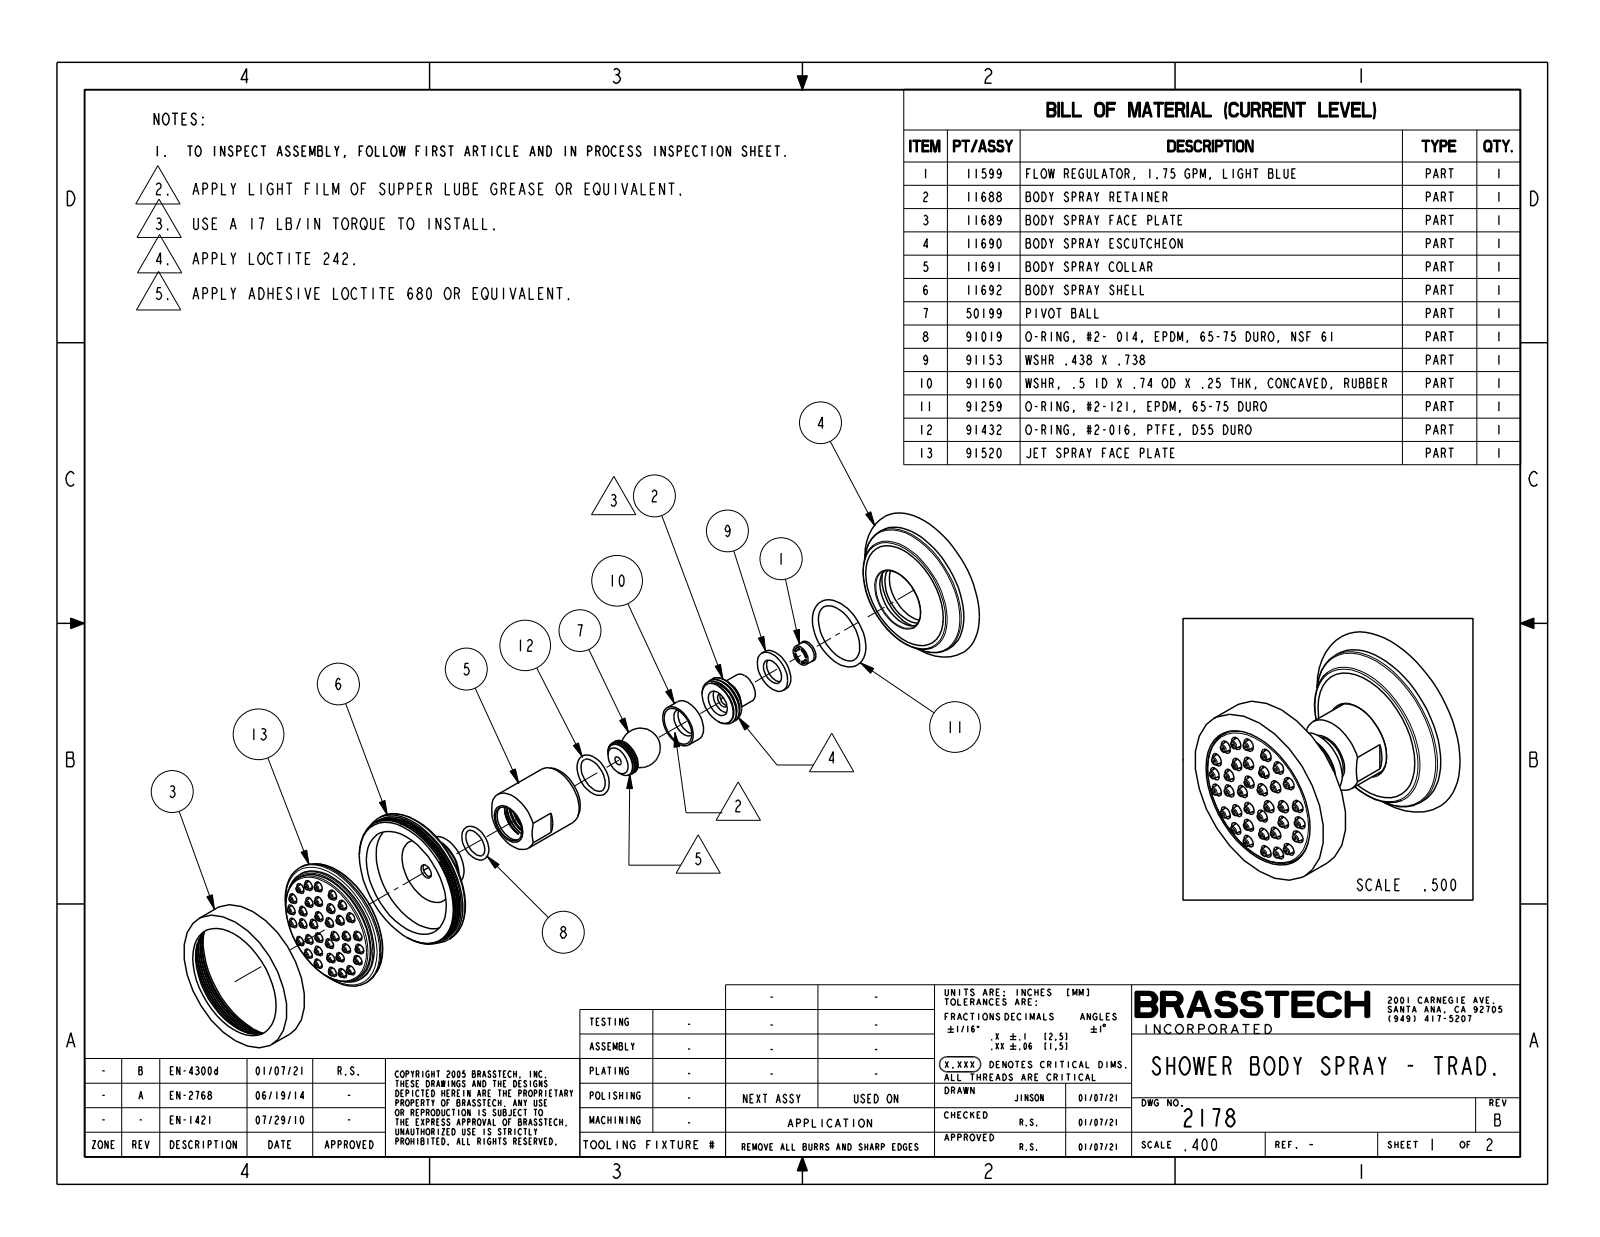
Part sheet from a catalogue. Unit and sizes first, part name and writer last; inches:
Units: inches
Overall size (bounding box): 2.696 × 2.696 × 2.674
Round holes (diameter × count): ⌀0.039 ×36, ⌀0.181 ×31, ⌀1.092 ×1, ⌀2.022 ×1
Round bosses / shafts (diameter × count): ⌀2.5 ×1, ⌀2.336 ×1, ⌀1.992 ×1, ⌀1.062 ×1, ⌀0.9 ×1, ⌀0.315 ×1
Partial cylindrical surfaces — rounded edges, fillets, slot ends (radius × count): R0.091 ×5
Main face-to-face distances: 1.39, 0.47, 0.92, 2.116, 1.646, 0.726, 0.98, 1.24, 0.77, 0.15
Hole centre spacings: 0.827, 1.432, 0.541, 0.593, 1.285, 1.544, 1.041, 1.106
Volume: 6.255 in³ · Surface area: 34.32 in²
Bodies: 1 solid, 455 faces (48 planar, 155 cylindrical, 252 other)
Part name (STEP PRODUCT): 2178
STEP written by: CREO PARAMETRIC BY PTC INC, 2018400 (CONFIG_CONTROL_DESIGN)
